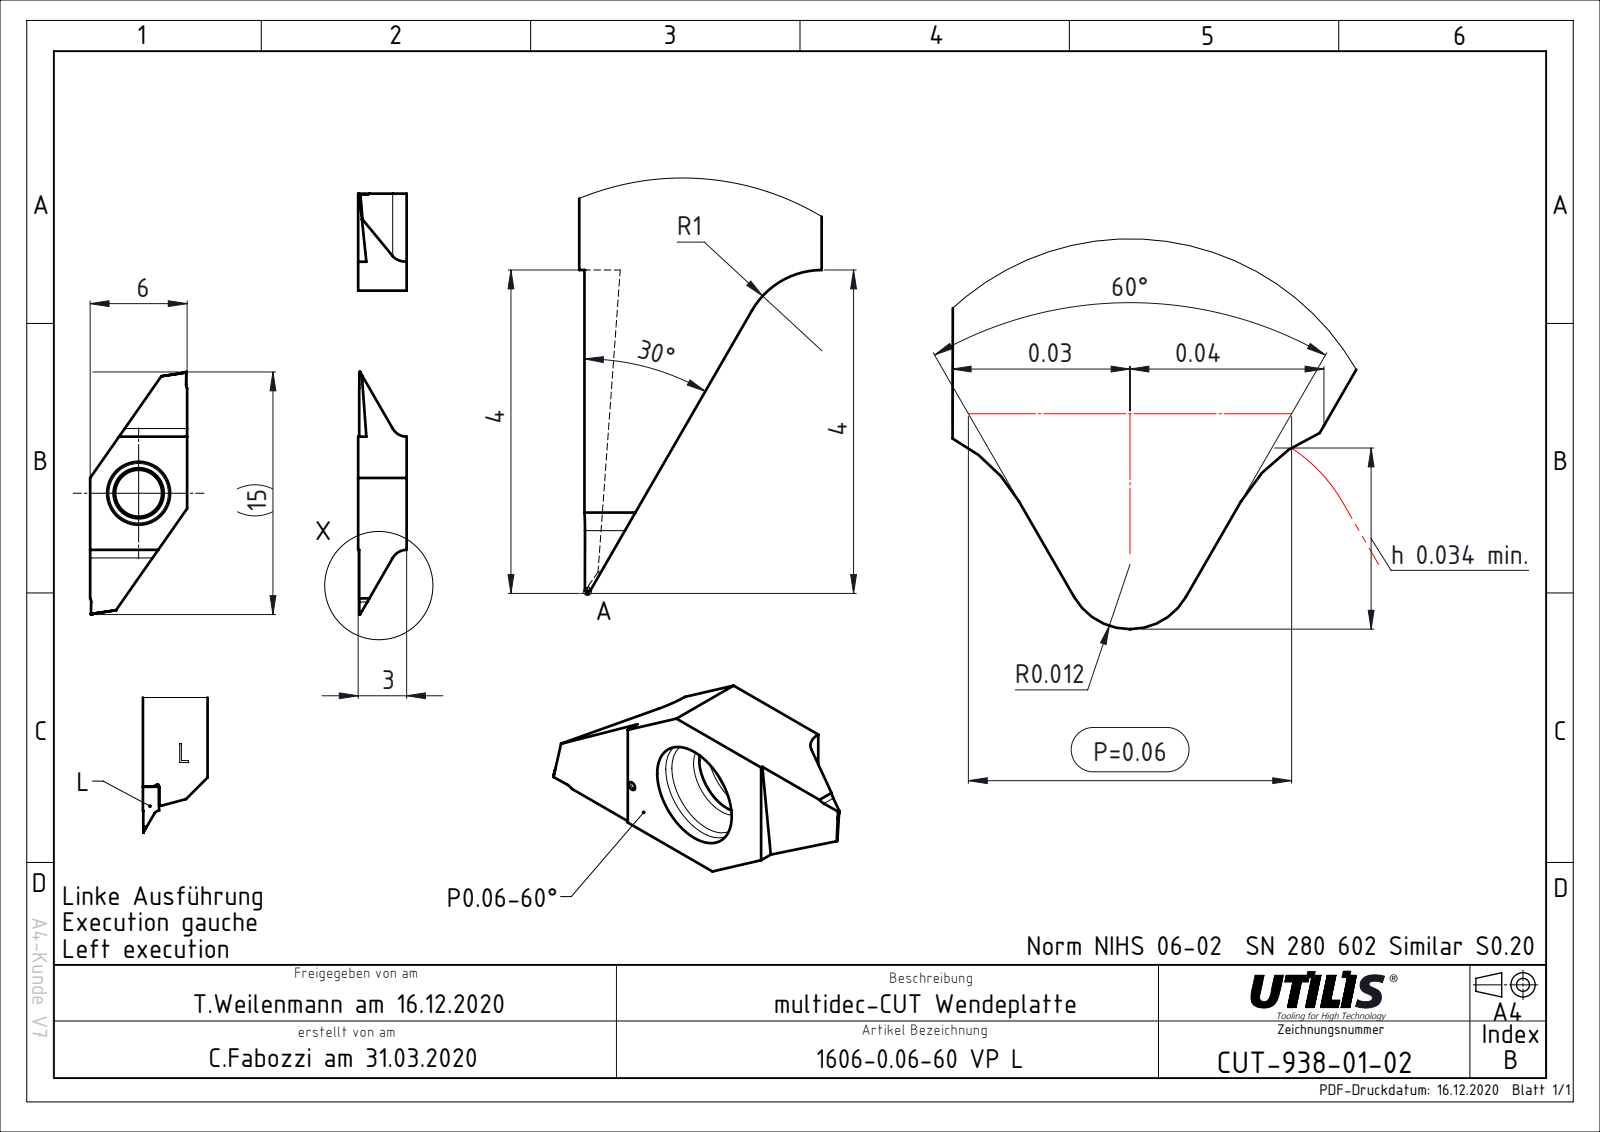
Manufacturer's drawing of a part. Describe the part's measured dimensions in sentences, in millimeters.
The part is named "CUT-938-01; ASME Y14.5". Its 3-D file was written by "FormatWorks Professional (AP242_MANAGED_MODEL_BASED_3D_ENGINEERING_MIM_LF)". It is 1 solid with 36 faces: 22 planar, 14 cylindrical and 0 other. Overall it measures 15 by 6 by 3 millimeters. Its volume is 123 cubic millimeters and its surface area 208 square millimeters. Round holes: 1 of diameter 2.9. Partial cylindrical surfaces (rounded edges, fillets, slot ends): 2 of radius 1. The main face-to-face distances are 6, 3, 9, 7, 12, 7.19.
